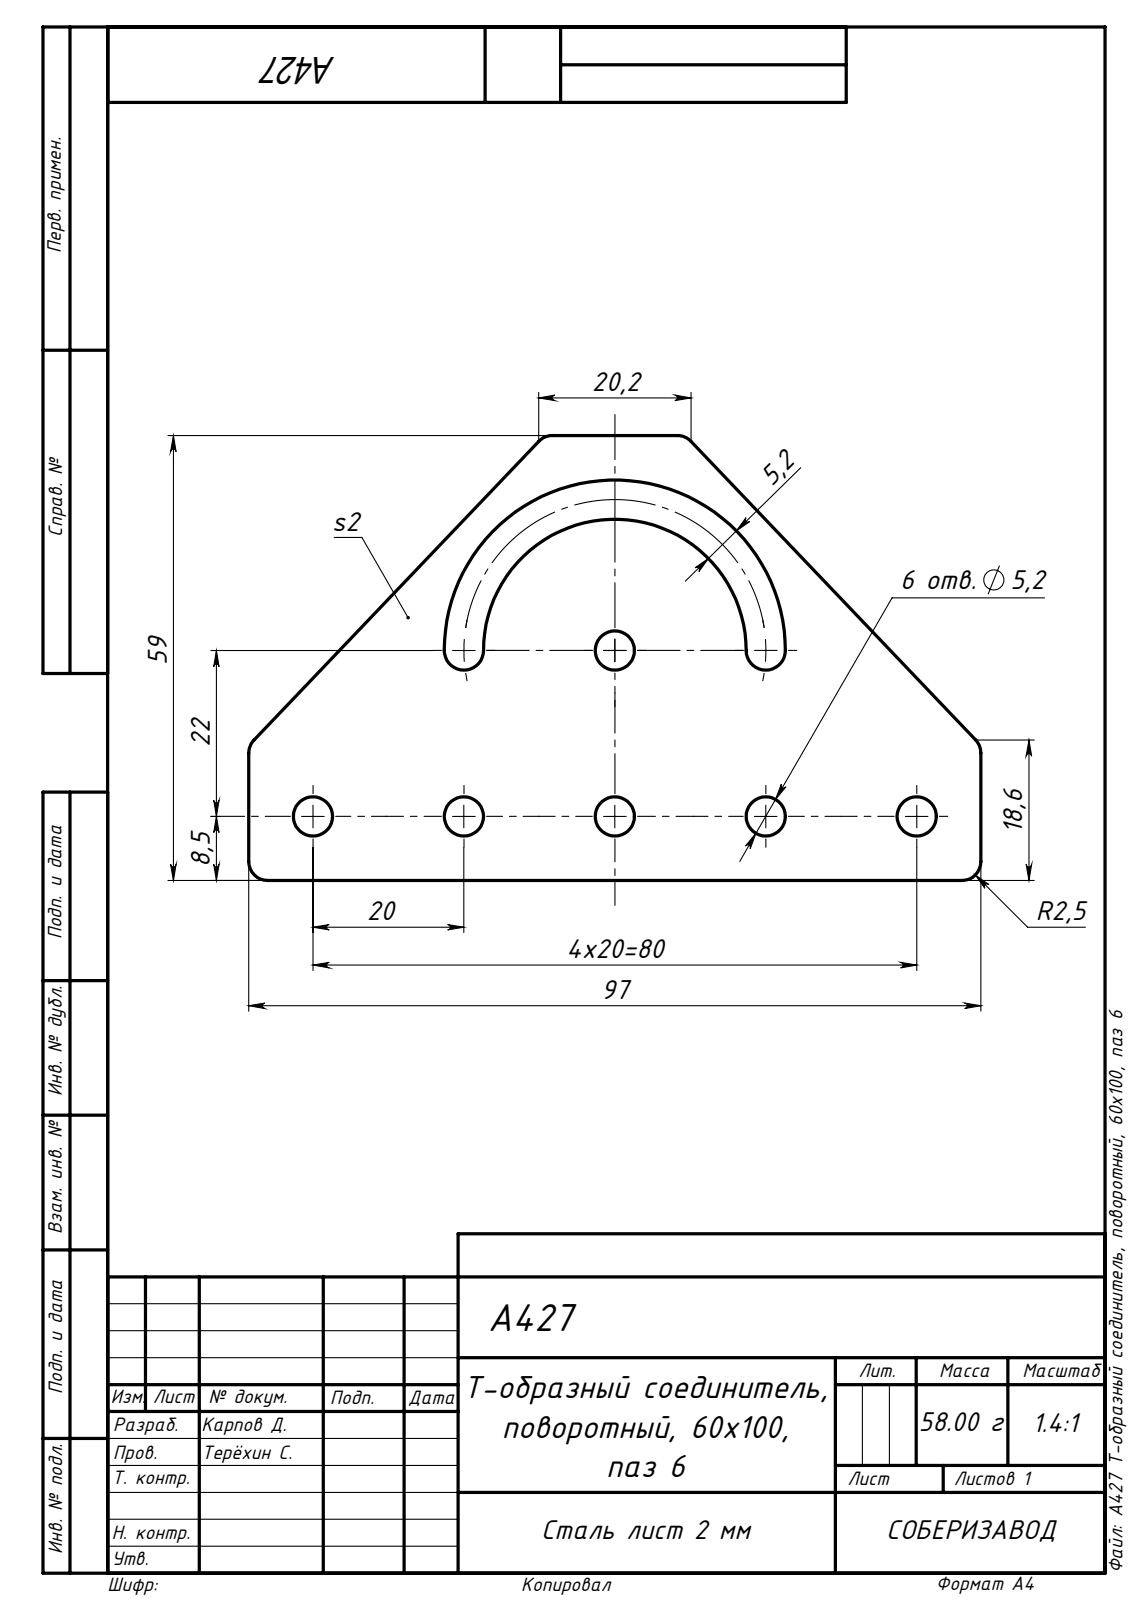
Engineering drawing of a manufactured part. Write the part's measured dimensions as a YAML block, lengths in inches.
step_written_by: "SolidWorks 2020 (AUTOMOTIVE_DESIGN)"
units: inches
bodies: {solids: 1, faces: 30, planar: 8, cylindrical: 22, other: 0}
overall_size: [3.819, 2.323, 0.079]
volume: 0.444
surface_area: 12.83
round_holes:
  - {diameter: 0.205, count: 6}
partial_cylinders:
  - {radius: 0.098, count: 6}
  - {radius: 0.102, count: 2}
  - {radius: 0.685, count: 1}
  - {radius: 0.89, count: 1}
face_to_face_distances: [0.079, 2.323, 3.819]
hole_center_spacings: [0.787, 1.575, 1.17, 1.797, 2.362, 0.866, 3.15]
